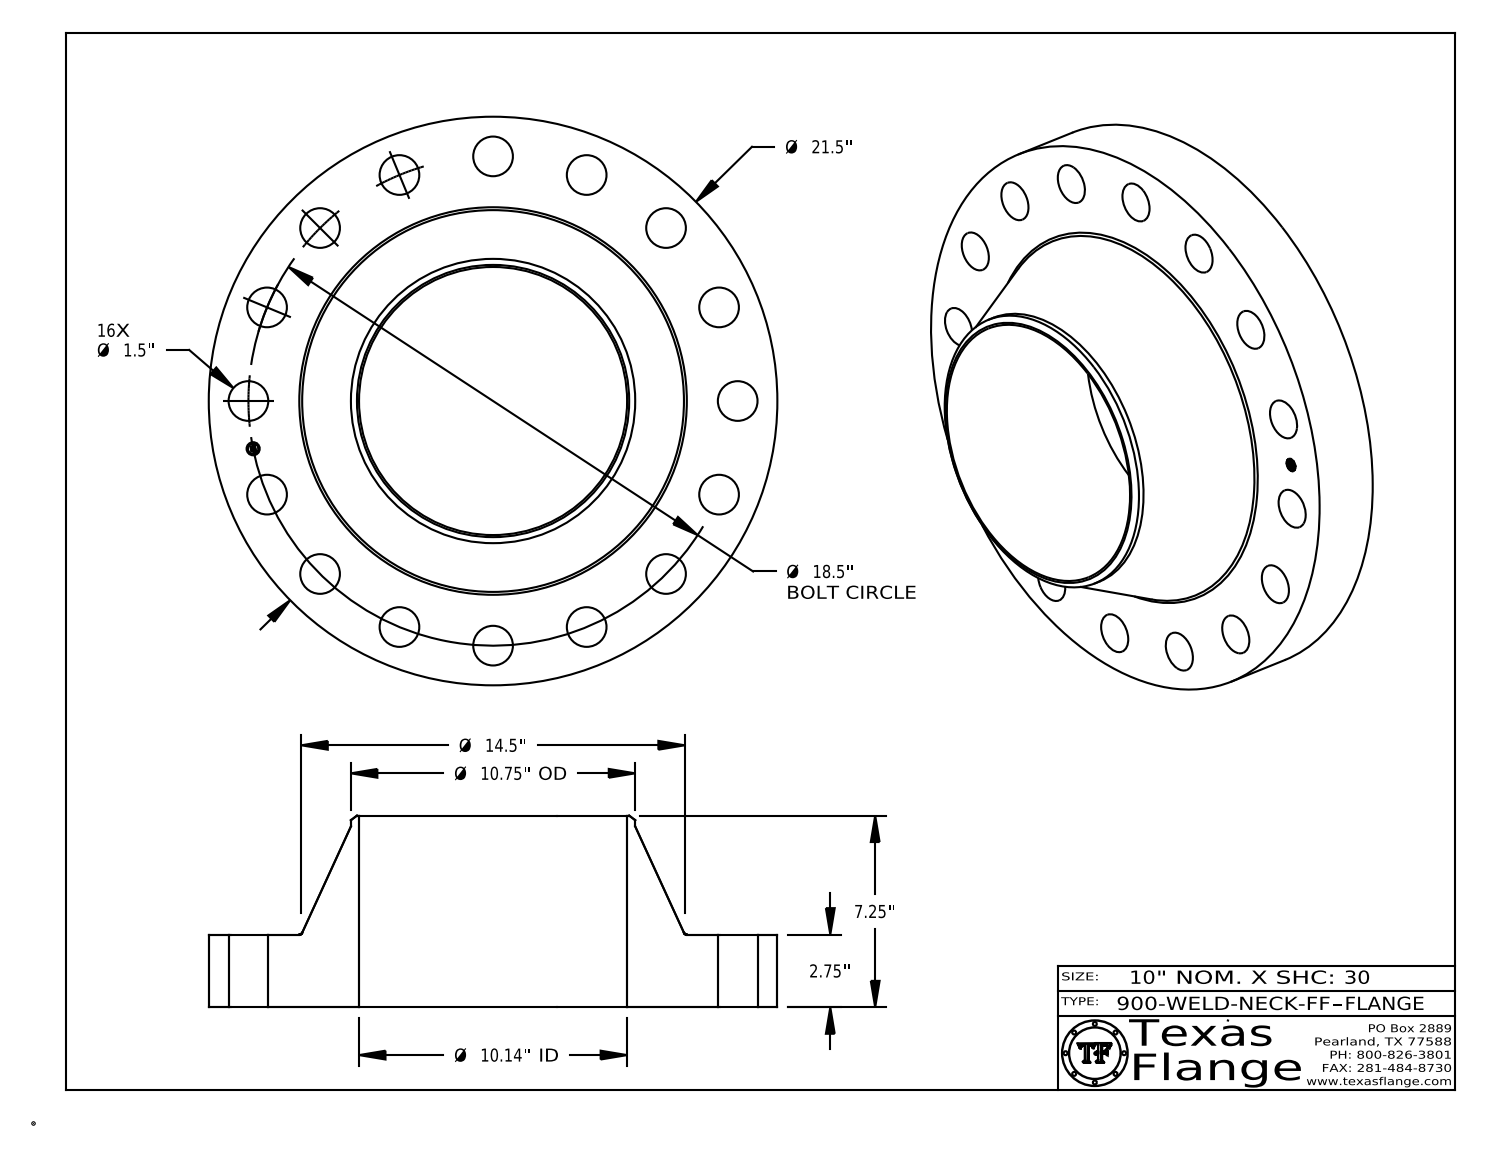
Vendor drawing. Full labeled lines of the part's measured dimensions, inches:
Part name (STEP PRODUCT): 900-WELD-NECK-FF
STEP written by: CATIA V5 STEP AP214 (AUTOMOTIVE_DESIGN)
Units: inches
Bodies: 1 solid, 432 faces (368 planar, 58 cylindrical, 6 other)
Overall size (bounding box): 21.5 × 21.5 × 7.25
Volume: 887.9 in³ · Surface area: 1 245 in²
Round holes (diameter × count): ⌀1.5 ×16, ⌀0.495 ×1, ⌀10.136 ×1
Round bosses / shafts (diameter × count): ⌀0.03 ×8, ⌀21.5 ×1, ⌀10.75 ×1, ⌀0.39 ×1
Main face-to-face distances: 2.75, 7.25, 4.5, 2.735, 0.015, 4.515, 0.148, 0.145, 0.027, 0.096
Hole centre spacings: 15.382, 7.08, 9.25, 13.081, 3.609, 3.609, 10.278, 10.278
